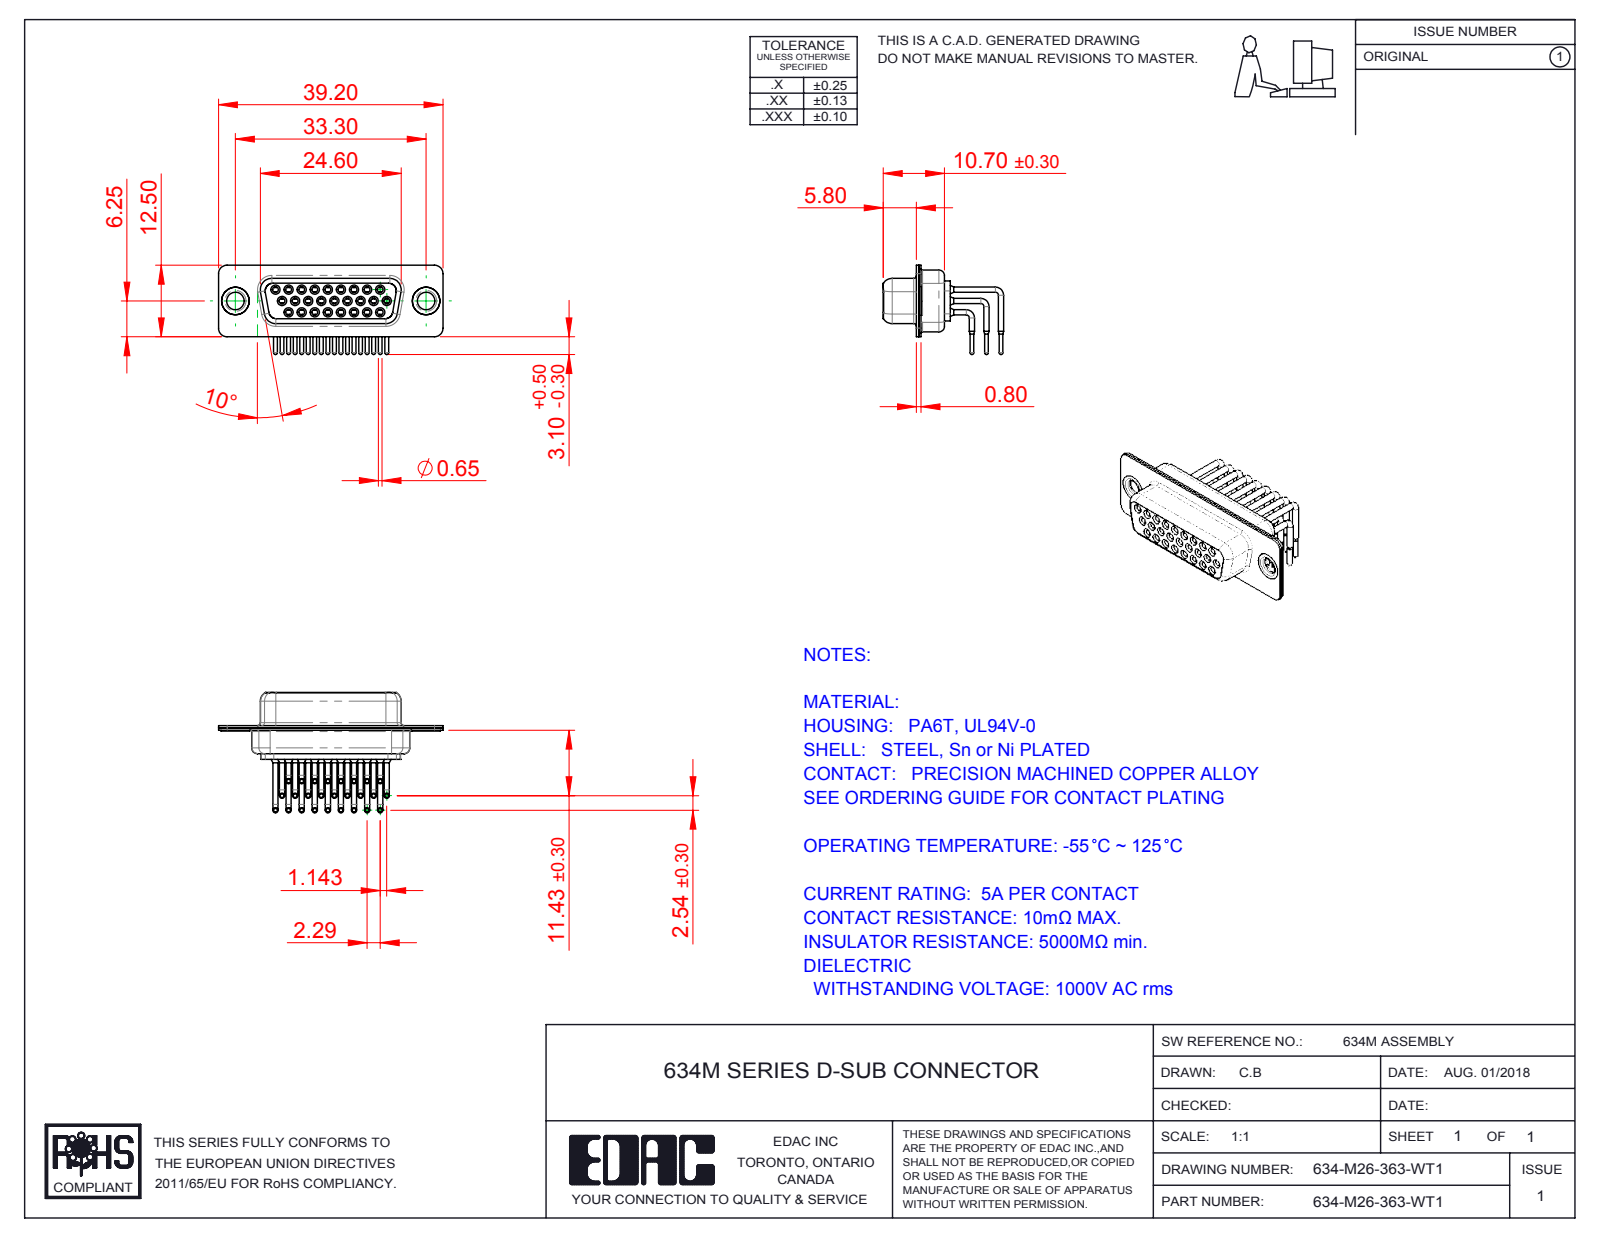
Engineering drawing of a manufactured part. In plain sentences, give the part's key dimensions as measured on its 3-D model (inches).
The part is named "634M Contact Row 1; 634M Shell Rear_26 Contacts; 634M Contact Row 2; 634M Thru Hole Rivet (+4 more)". Its 3-D file was written by "SolidWorks 2016 (CONFIG_CONTROL_DESIGN)". It is 31 solids with 1631 faces: 457 planar, 719 cylindrical and 455 other. Overall it measures 1.543 by 0.828 by 0.614 inches. Its volume is 0.15 cubic inches and its surface area 12.9 square inches. Round holes: 26 of diameter 0.039, 26 of diameter 0.043, 26 of diameter 0.067, 26 of diameter 0.071, 26 of diameter 0.079, 2 of diameter 0.12, 2 of diameter 0.157, 2 of diameter 0.189. Round bosses or shafts: 52 of diameter 0.035, 26 of diameter 0.063, 26 of diameter 0.059, 26 of diameter 0.026, 2 of diameter 0.197, 2 of diameter 0.193, 2 of diameter 0.14, 1 of diameter 0.079. Partial cylindrical surfaces (rounded edges, fillets, slot ends): 16 of radius 0.059, 12 of radius 0.079, 8 of radius 0.053, 8 of radius 0.063, 4 of radius 0.01, 4 of radius 0.02, 4 of radius 0.024, 4 of radius 0.026. The main face-to-face distances are 0.016, 0.057, 0.352, 0.335, 0.075, 0.091, 0.031, 0.244, 0.018, 0.278. The hole center spacings are 0.156, 0.09, 0.18, 0.238, 0.09, 0.324, 0.27, 0.238.
